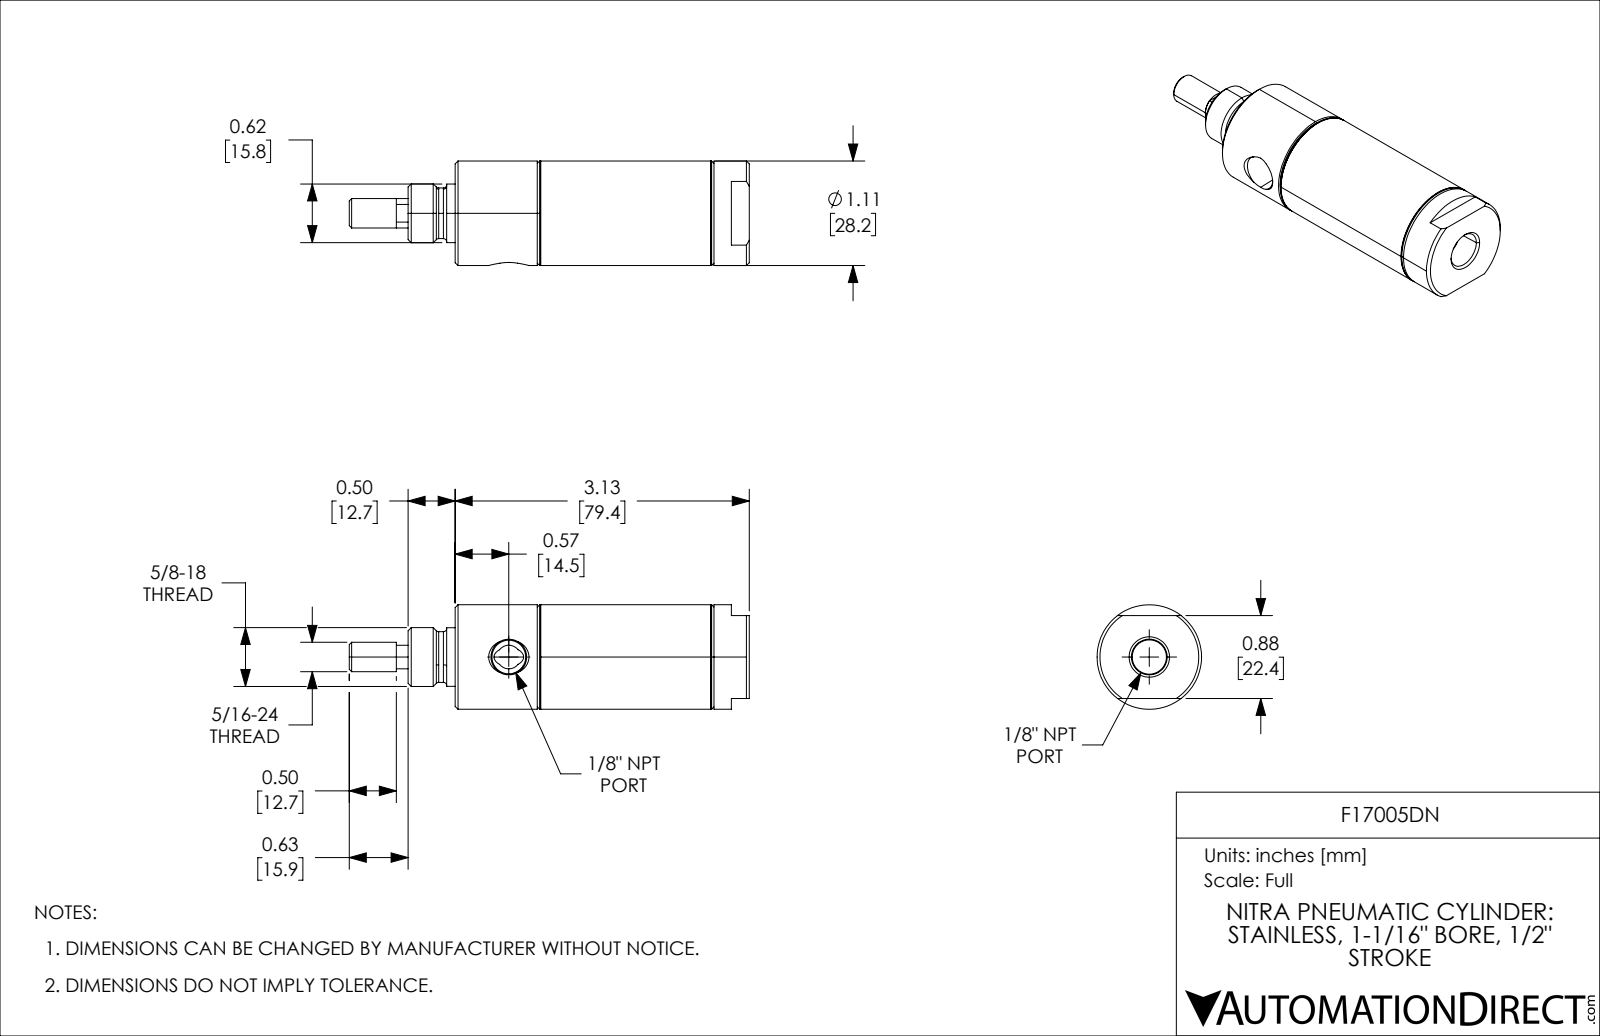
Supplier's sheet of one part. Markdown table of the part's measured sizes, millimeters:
| quantity | value |
| --- | --- |
| part name | F17005DN_5; F17005DN_7; F17005DN_9; F17005DN (+1 more) |
| STEP written by | SolidWorks 2021 (CONFIG_CONTROL_DESIGN) |
| units | millimeters |
| bodies | 4 solids, 125 faces (25 planar, 44 cylindrical, 56 other) |
| overall size | 107.95 × 28.19 × 28.19 |
| volume | 41 841 mm³ |
| surface area | 22 313 mm² |
| round holes (diameter × count) | 8.53 × 1, 9.25 × 1, 19.05 × 1, 25.7 × 1 |
| round bosses / shafts (diameter × count) | 28.19 × 1, 27.23 × 1, 15.88 × 1, 15.81 × 1, 13.68 × 1, 7.94 × 1, 7.92 × 1 |
| partial cylindrical surfaces (radius × count) | 3.17 × 1 |
| main face-to-face distances | 12.7, 22.22, 34.92, 41.28, 50.8, 38.1, 15.88, 28.58, 63.5, 79.38 |
